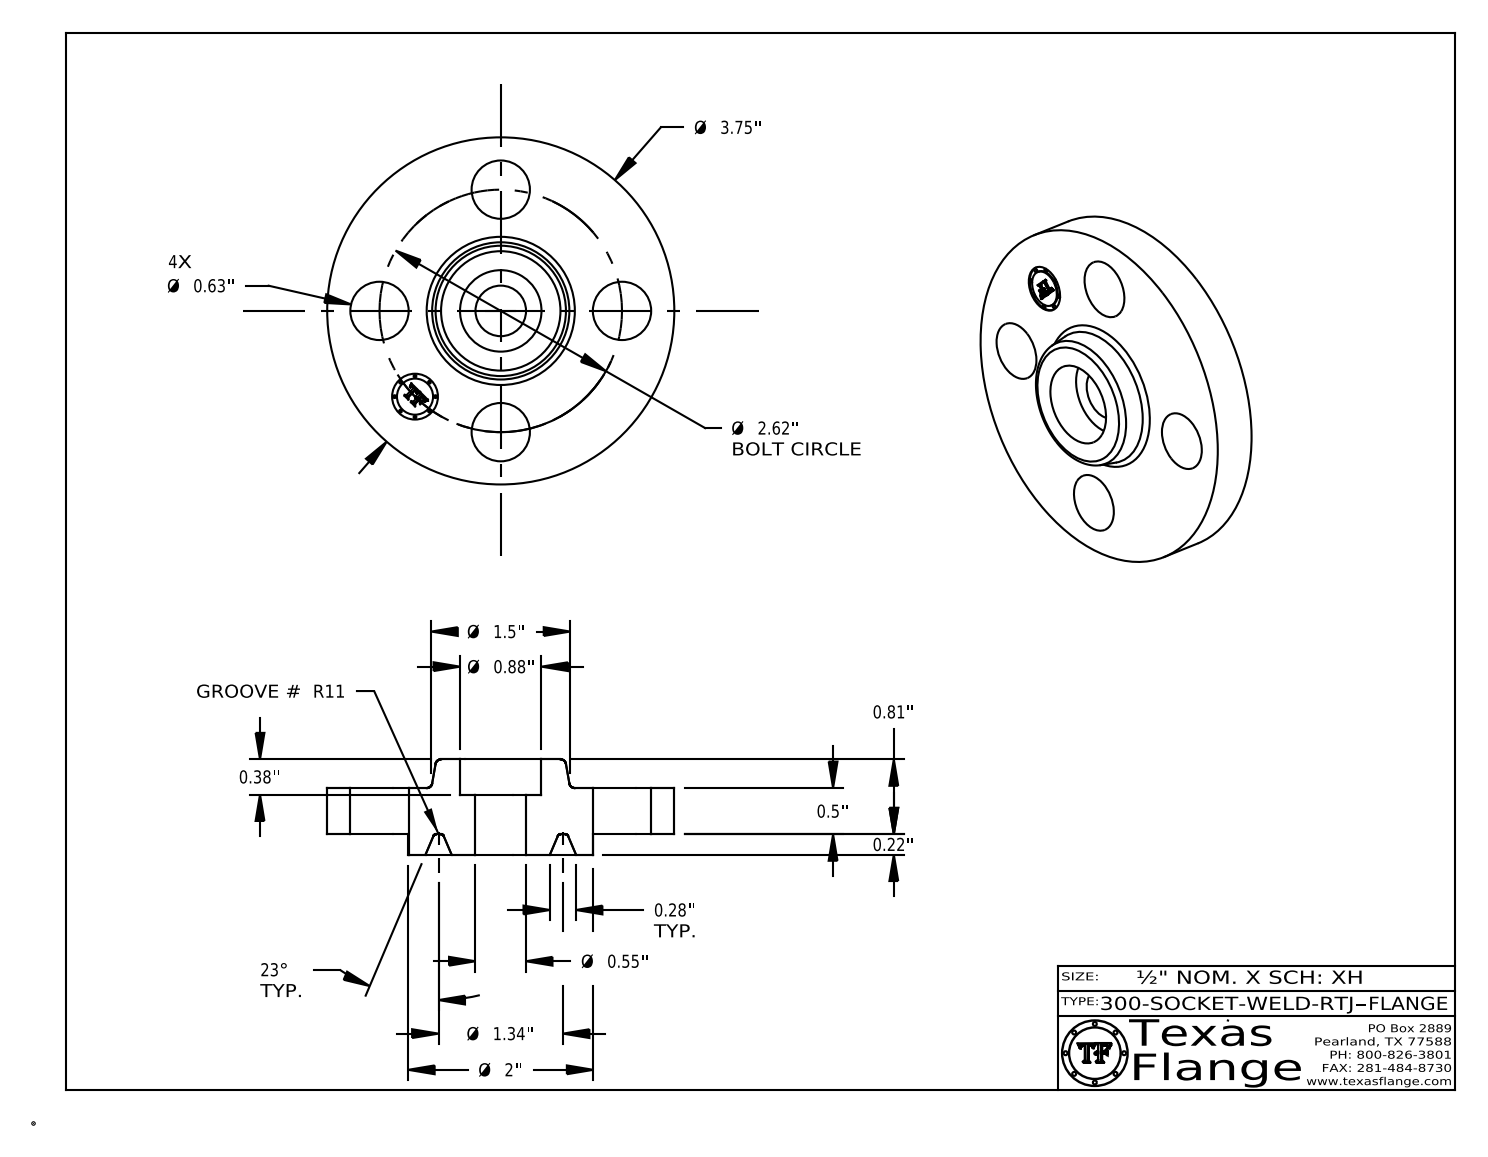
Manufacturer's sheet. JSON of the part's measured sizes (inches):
{"part_name": "300-SOCKET-WELD-RTJ", "step_written_by": "CATIA V5 STEP AP214 (AUTOMOTIVE_DESIGN)", "units": "inches", "bodies": {"solids": 1, "faces": 426, "planar": 372, "cylindrical": 40, "other": 14}, "overall_size": [3.75, 3.75, 1.029], "volume_in3": 5.538, "surface_area_in2": 34.82, "round_holes": [[0.63, 4], [0.495, 1], [0.546, 1], [0.88, 1]], "round_bosses_or_shafts": [[0.03, 8], [3.75, 1], [2, 1], [0.39, 1]], "face_to_face_distances": [0.5, 0.219, 0.719, 1.029, 0.81, 0.31, 0.07, 0.649, 0.43, 0.38], "hole_center_spacings": [1.31, 1.852, 1.003, 2.42, 2.62, 1.31]}
